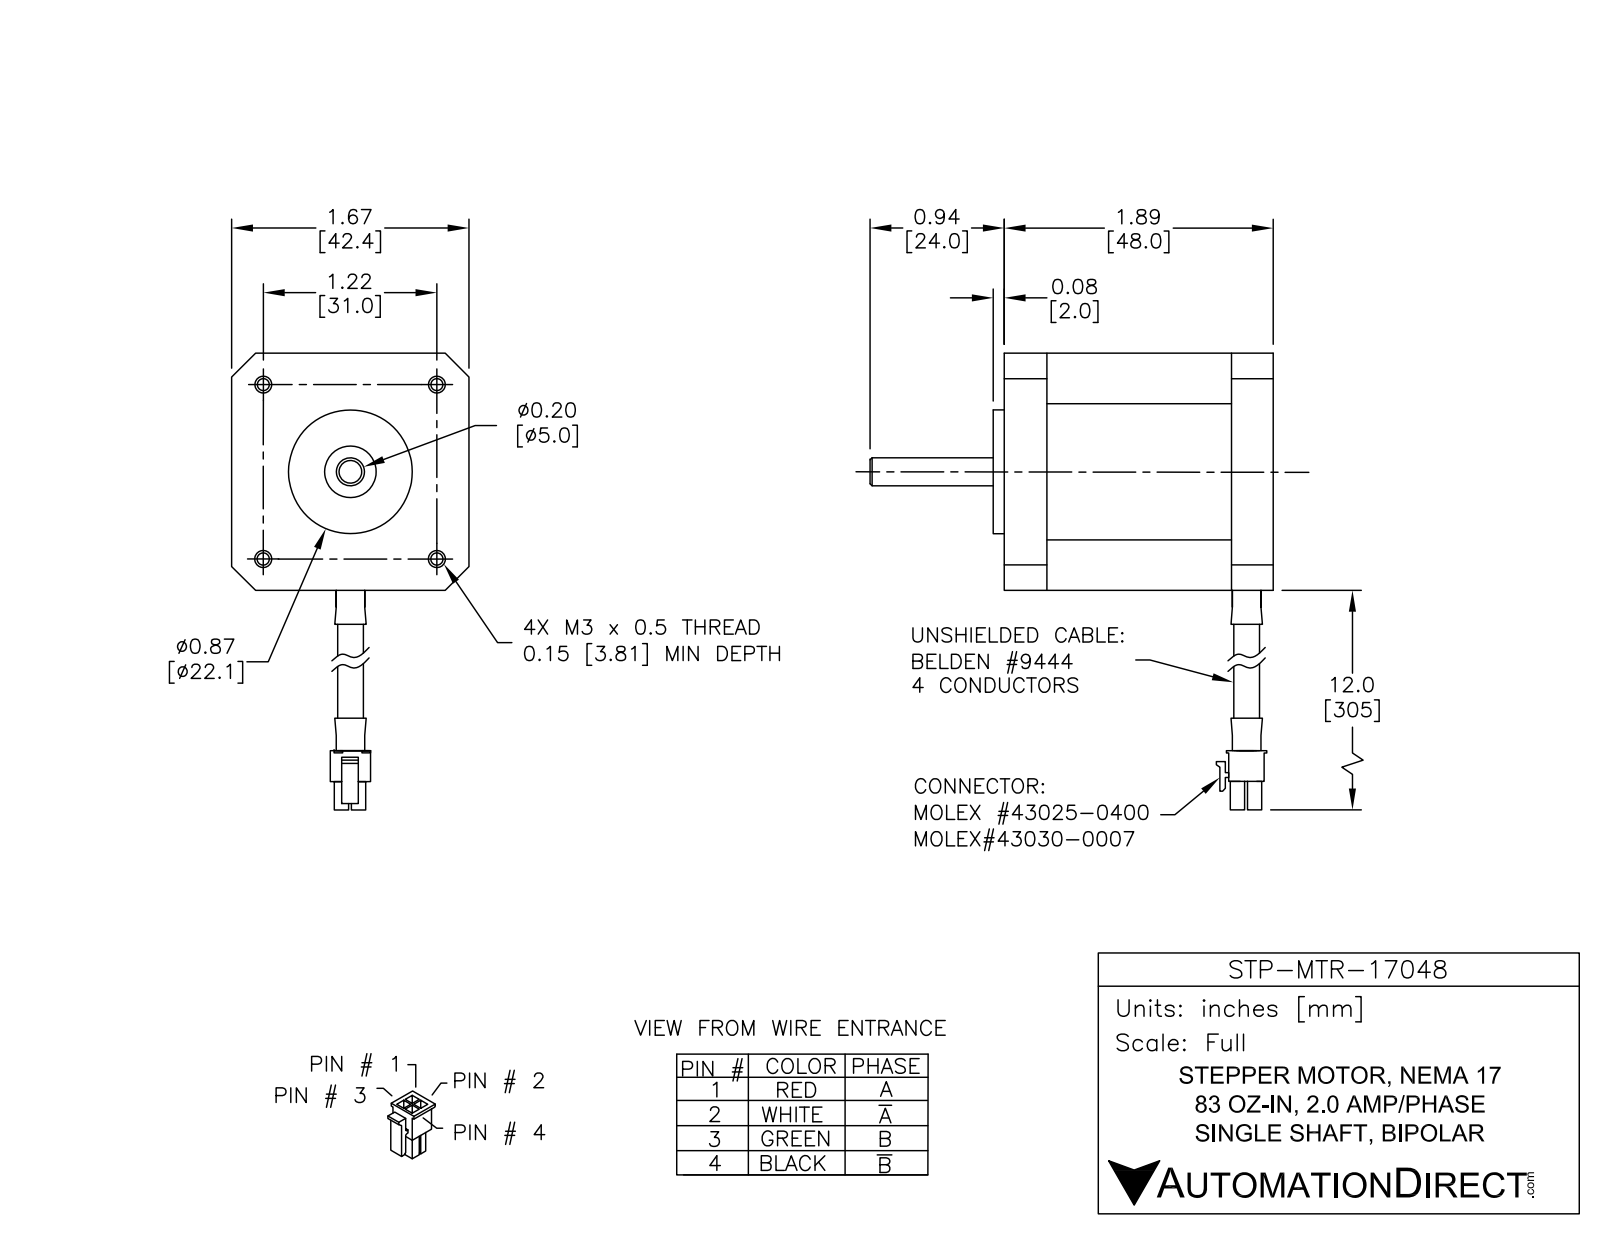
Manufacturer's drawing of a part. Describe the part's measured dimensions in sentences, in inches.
The part is named "STP-MTR-17048". Its 3-D file was written by "SolidWorks 2014 (AUTOMOTIVE_DESIGN)". It is 1 solid with 40 faces: 16 planar, 24 cylindrical and 0 other. Overall it measures 5.266 by 2.83 by 1.66 inches. Its volume is 5.152 cubic inches and its surface area 21.68 square inches. Round holes: 4 of diameter 0.086. Round bosses or shafts: 4 of diameter 0.038, 1 of diameter 0.866, 1 of diameter 0.197. Partial cylindrical surfaces (rounded edges, fillets, slot ends): 1 of radius 1.06. The main face-to-face distances are 1.66, 1.89, 1.969, 0.079, 2.83, 0.94, 0.861, 0.03, 1.86, 1.939. The hole center spacings are 1.22, 1.725.
